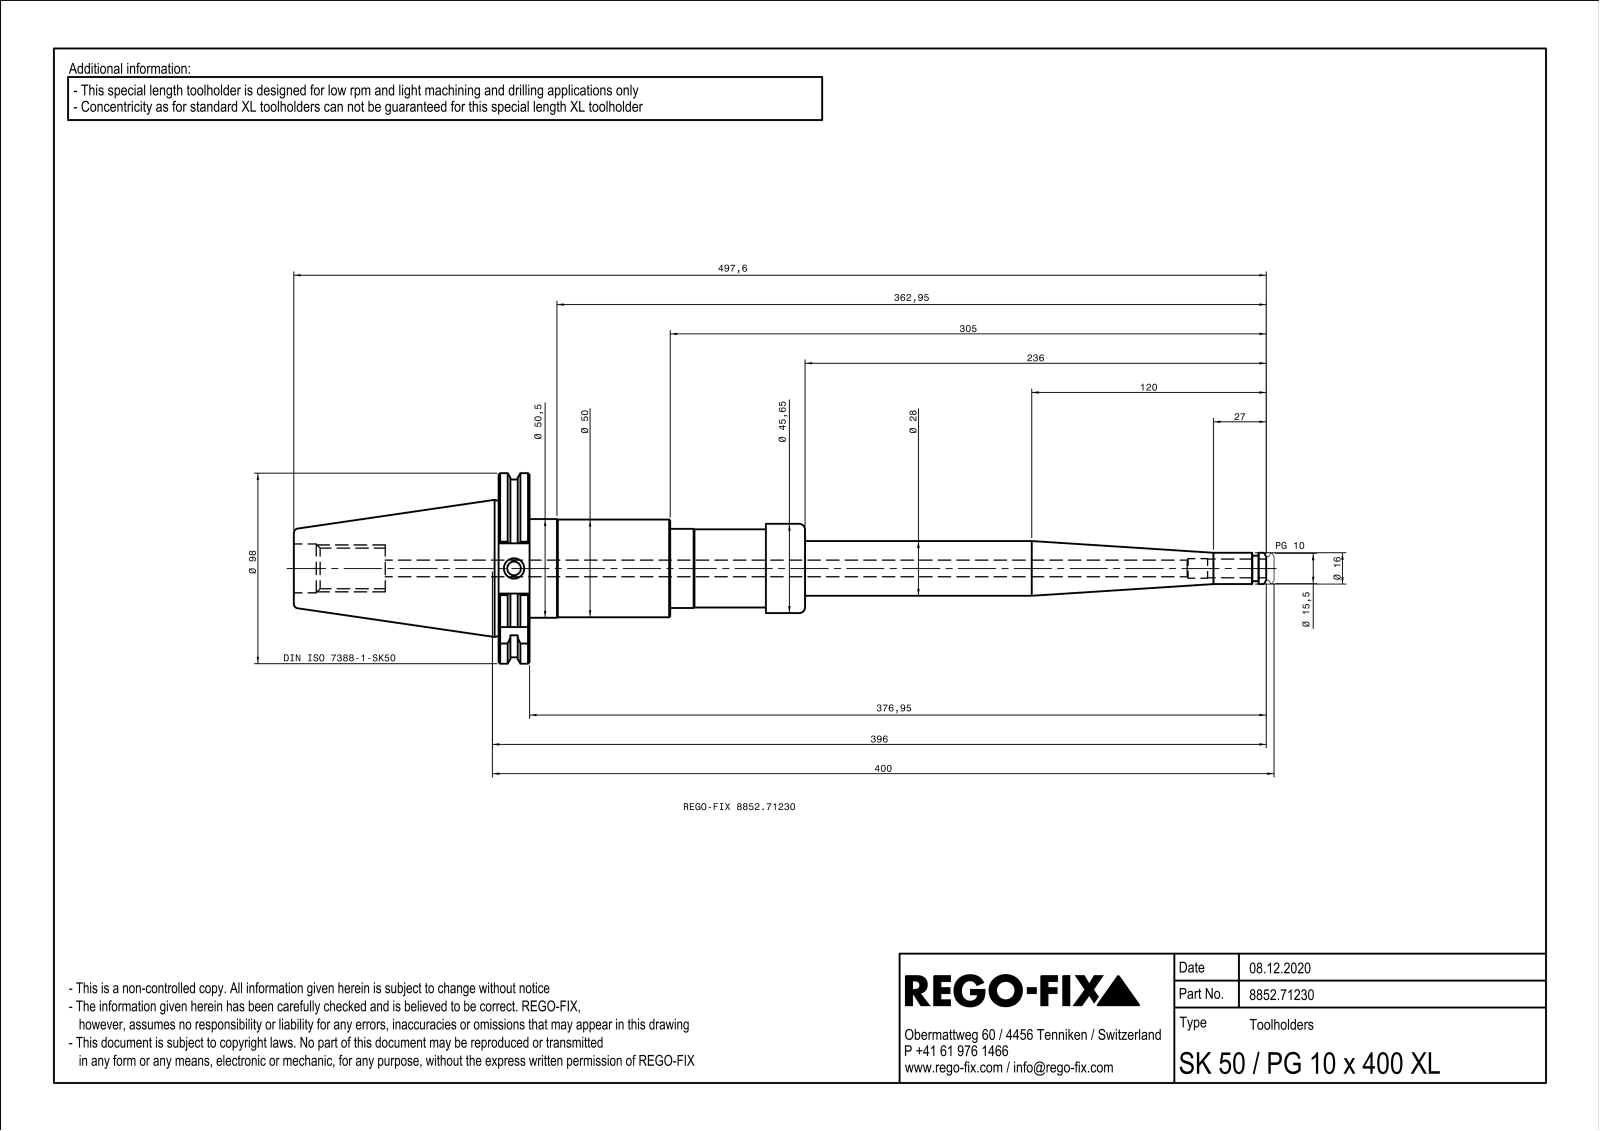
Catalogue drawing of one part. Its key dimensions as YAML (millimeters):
part_name: "NOCUT"
step_written_by: "SIEMENS PLM Software Solid Edge ST10 (AUTOMOTIVE_DESIGN)"
units: millimeters
bodies: {solids: 1, faces: 177, planar: 59, cylindrical: 42, other: 76}
overall_size: [497.6, 97.5, 93.58]
volume: 615252
surface_area: 102821
round_holes:
  - {diameter: 10, count: 2}
  - {diameter: 7, count: 1}
  - {diameter: 9, count: 1}
  - {diameter: 20.75, count: 1}
  - {diameter: 25, count: 1}
  - {diameter: 29, count: 1}
  - {diameter: 38.38, count: 1}
  - {diameter: 40.05, count: 1}
  - {diameter: 43.3, count: 1}
round_bosses_or_shafts:
  - {diameter: 91, count: 1}
  - {diameter: 50.5, count: 1}
  - {diameter: 50, count: 1}
  - {diameter: 45.65, count: 1}
  - {diameter: 40.5, count: 1}
  - {diameter: 40, count: 1}
  - {diameter: 34, count: 1}
  - {diameter: 33, count: 1}
partial_cylinders:
  - {radius: 0.5, count: 5}
  - {radius: 22.77, count: 1}
  - {radius: 48.75, count: 1}
face_to_face_distances: [15.85, 140.95, 156.8, 261.6, 120.65, 104.8, 6, 14, 69, 71.95]
